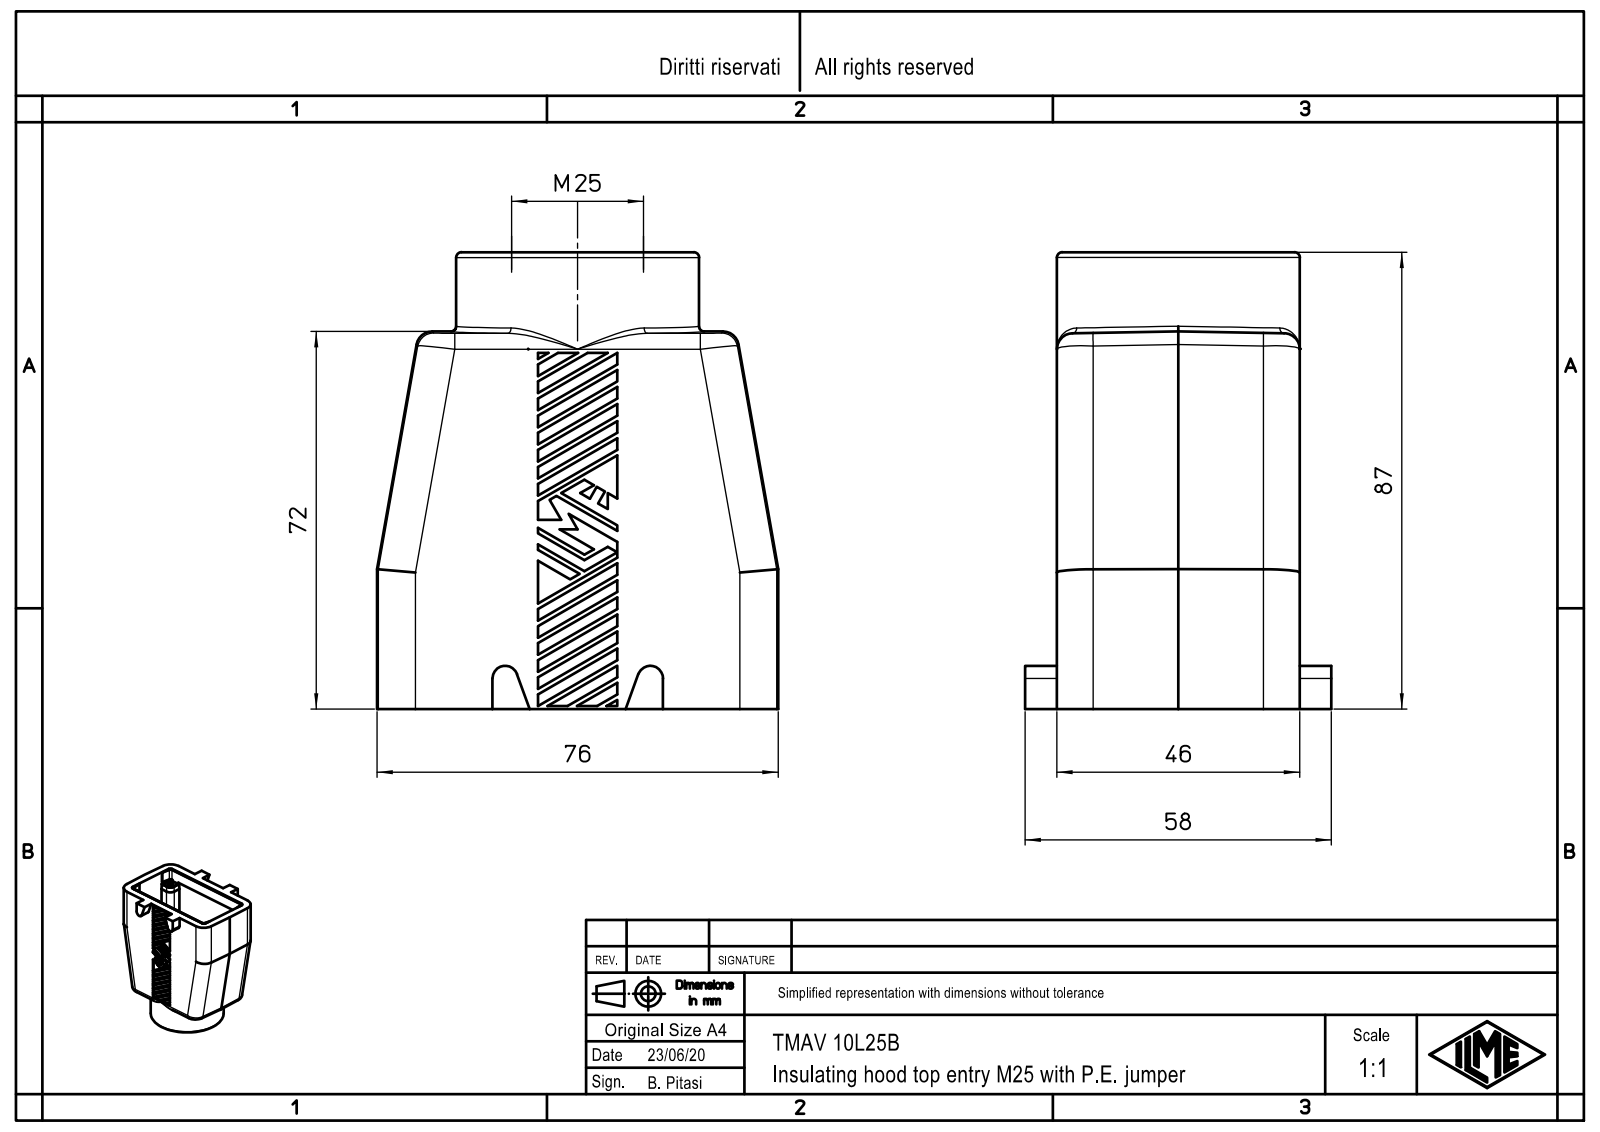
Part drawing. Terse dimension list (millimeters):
name: TMAV_10.25B
written by: Creo Elements/Direct Modeling 20.1B 02-Apr-2019 (C) Parametric Technology GmbH (AUTOMOTIVE_DESIGN)
unit: mm
bodies: 1 solid, 568 faces (404 planar, 82 cylindrical, 82 other)
size: 86.49 × 76 × 58
volume: 116 346 mm³; area: 41 367 mm²
holes: 4× ⌀3, 4× ⌀3.5, 1× ⌀21, 1× ⌀25
bosses: 4× ⌀4.8, 1× ⌀46
rounds: 12× R1.5, 8× R7, 6× R3, 4× R1.3, 4× R1.6, 4× R2, 4× R3.5, 2× R2.4
face distances: 46, 65.99, 0.5, 45.5, 5.6, 20.5, 86.49, 5.3, 5.8, 40.2
hole spacings: 31.54, 27, 57, 63.07
